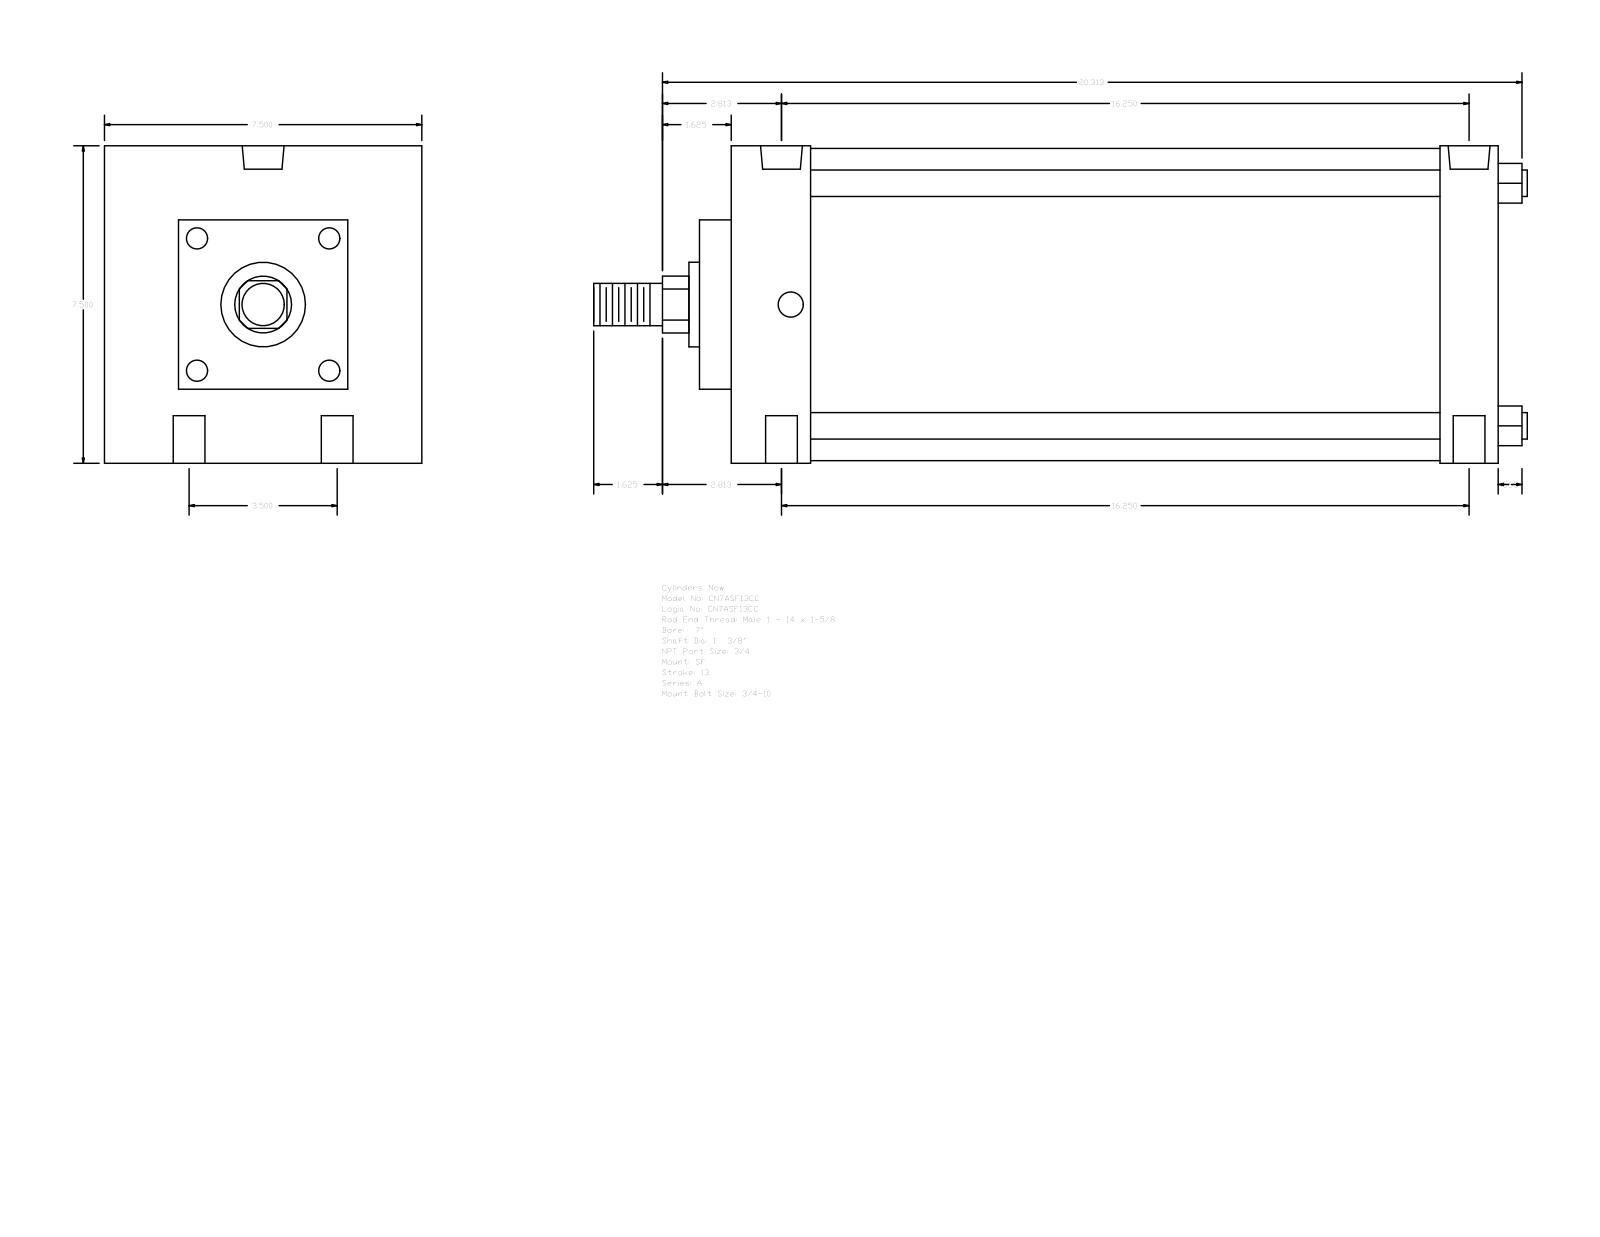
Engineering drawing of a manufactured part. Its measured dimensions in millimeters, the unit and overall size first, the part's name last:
Units: millimetres
Overall size (bounding box): 560.39 × 190.5 × 190.5
Round holes (diameter × count): ⌀19.05 ×4, ⌀15.08 ×2, ⌀25.12 ×2
Round bosses / shafts (diameter × count): ⌀15.88 ×4, ⌀187.32 ×1, ⌀50.8 ×1, ⌀34.92 ×1, ⌀25.4 ×1
Partial cylindrical surfaces — rounded edges, fillets, slot ends (radius × count): R17.06 ×1
Main face-to-face distances: 190.5, 460.38, 19.04, 479.42, 66.67, 444.5, 47.63, 425.46, 377.83, 412.75
Hole centre spacings: 44.45, 415.14, 412.75, 88.9, 422.22, 401.63
Bodies: 0 solids, 93 faces (67 planar, 26 cylindrical, 0 other)
Part name (STEP PRODUCT): A_SF__0700_1.375
STEP written by: GSSL Pune (CONFIG_CONTROL_DESIGN)
